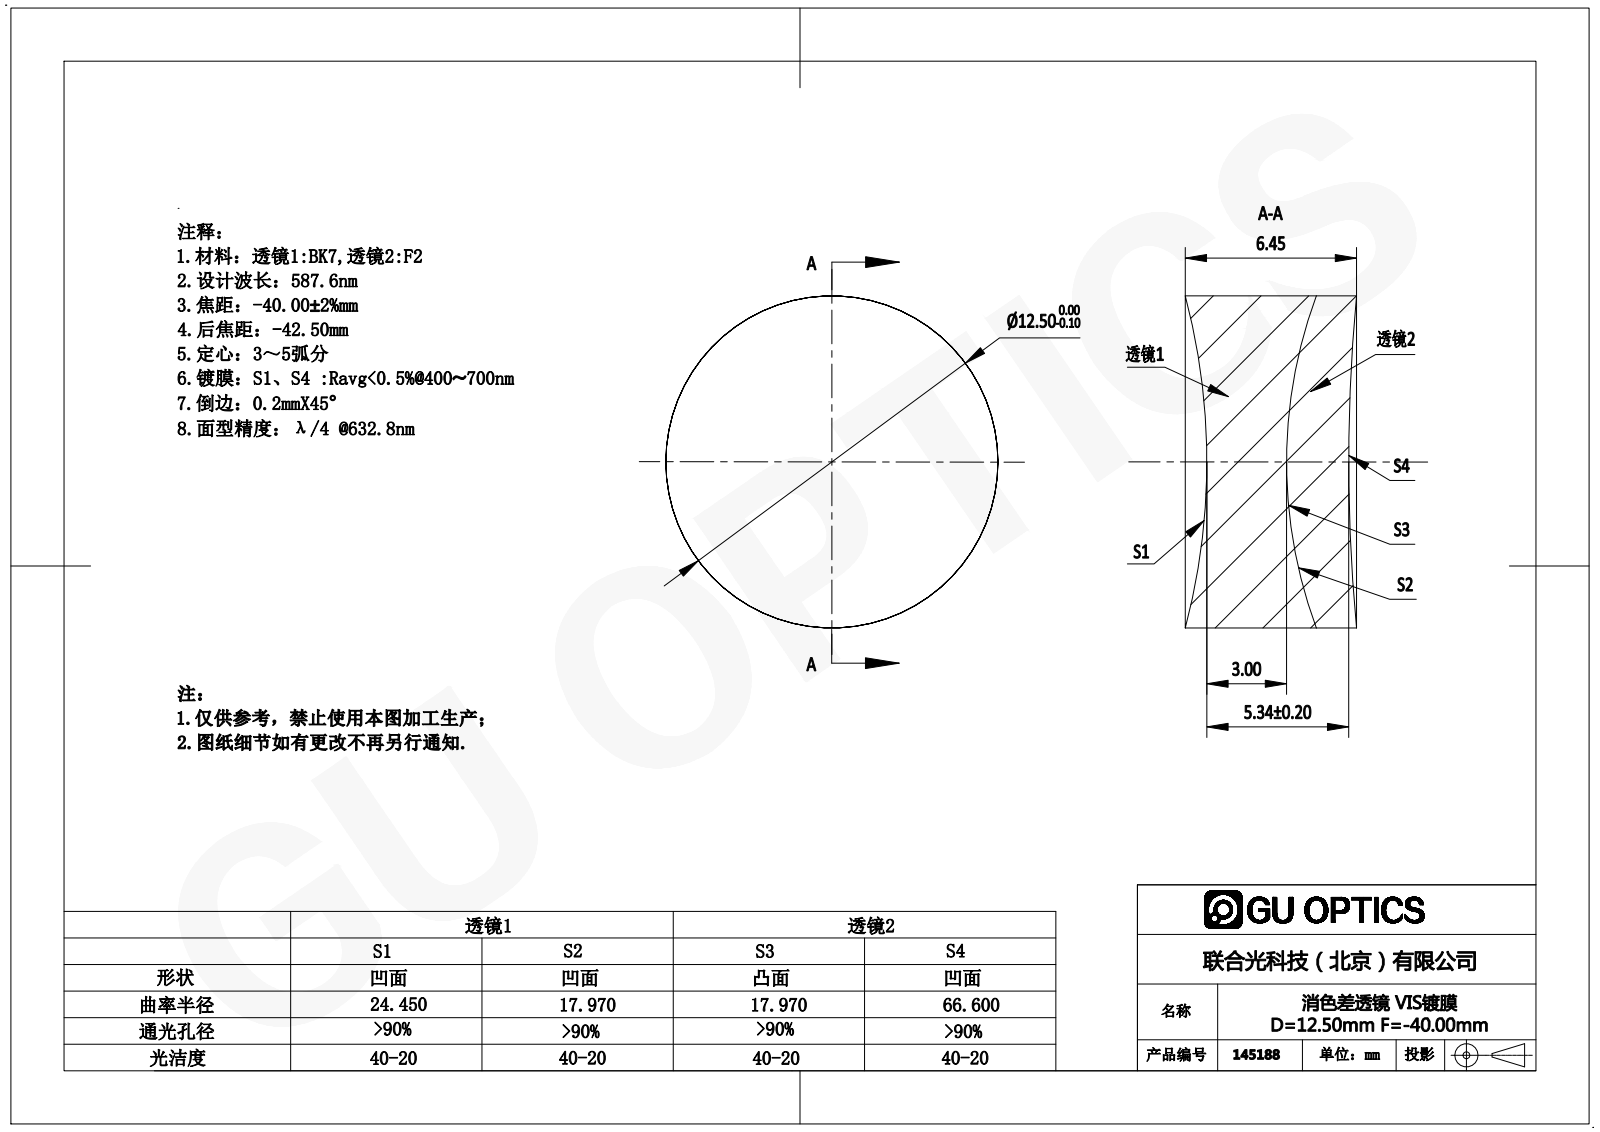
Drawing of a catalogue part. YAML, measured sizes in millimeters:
part_name: "145188"
step_written_by: "SolidWorks 2016 (AUTOMOTIVE_DESIGN)"
units: millimeters
bodies: {solids: 2, faces: 12, planar: 0, cylindrical: 4, other: 8}
overall_size: [12.5, 12.5, 6.45]
volume: 723
surface_area: 754
round_bosses_or_shafts:
  - {diameter: 12.5, count: 1}
